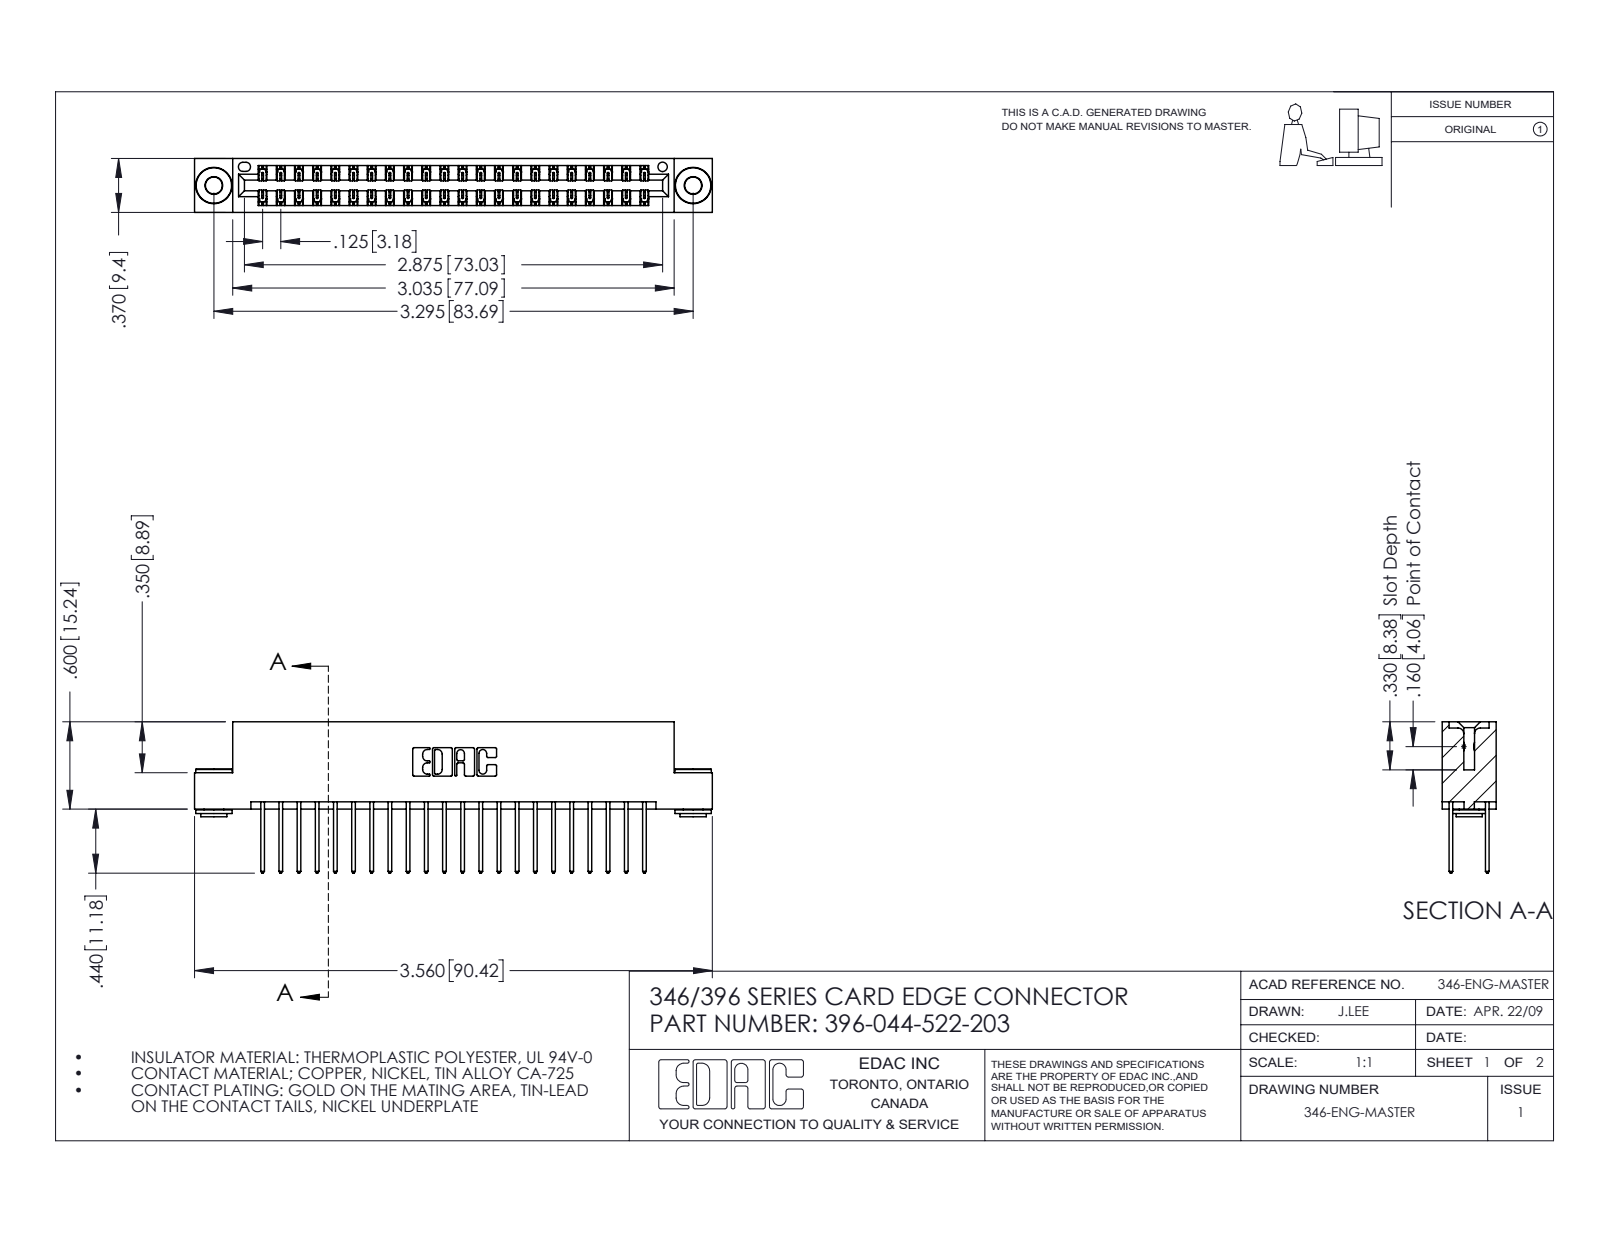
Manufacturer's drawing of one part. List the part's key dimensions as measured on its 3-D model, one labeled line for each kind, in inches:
Part name (STEP PRODUCT): 345-250-002_345-250-002-102; 346 Part_Flush Mounting Lugs - 0.156 Dia-TH; 345-292-001_345-293-122; 396-044-522-203
STEP written by: SolidWorks 2016 (CONFIG_CONTROL_DESIGN)
Units: inches
Bodies: 47 solids, 2448 faces (1626 planar, 814 cylindrical, 8 other)
Overall size (bounding box): 3.56 × 1.04 × 0.37
Volume: 0.537 in³ · Surface area: 19.39 in²
Round holes (diameter × count): ⌀0.116 ×2, ⌀0.156 ×2, ⌀0.064 ×1
Round bosses / shafts (diameter × count): ⌀0.25 ×2, ⌀0.18 ×2, ⌀0.136 ×2
Partial cylindrical surfaces — rounded edges, fillets, slot ends (radius × count): R0.006 ×66, R0.01 ×44, R0.01 ×22, R0.007 ×6, R0.031 ×6, R0.026 ×3, R0.014 ×2, R0.022 ×2
Main face-to-face distances: 0.048, 0.322, 0.25, 0.37, 0.025, 0.072, 0.298, 0.275, 0.148, 0.222
Hole centre spacings: 0.246, 3.087, 3.295
